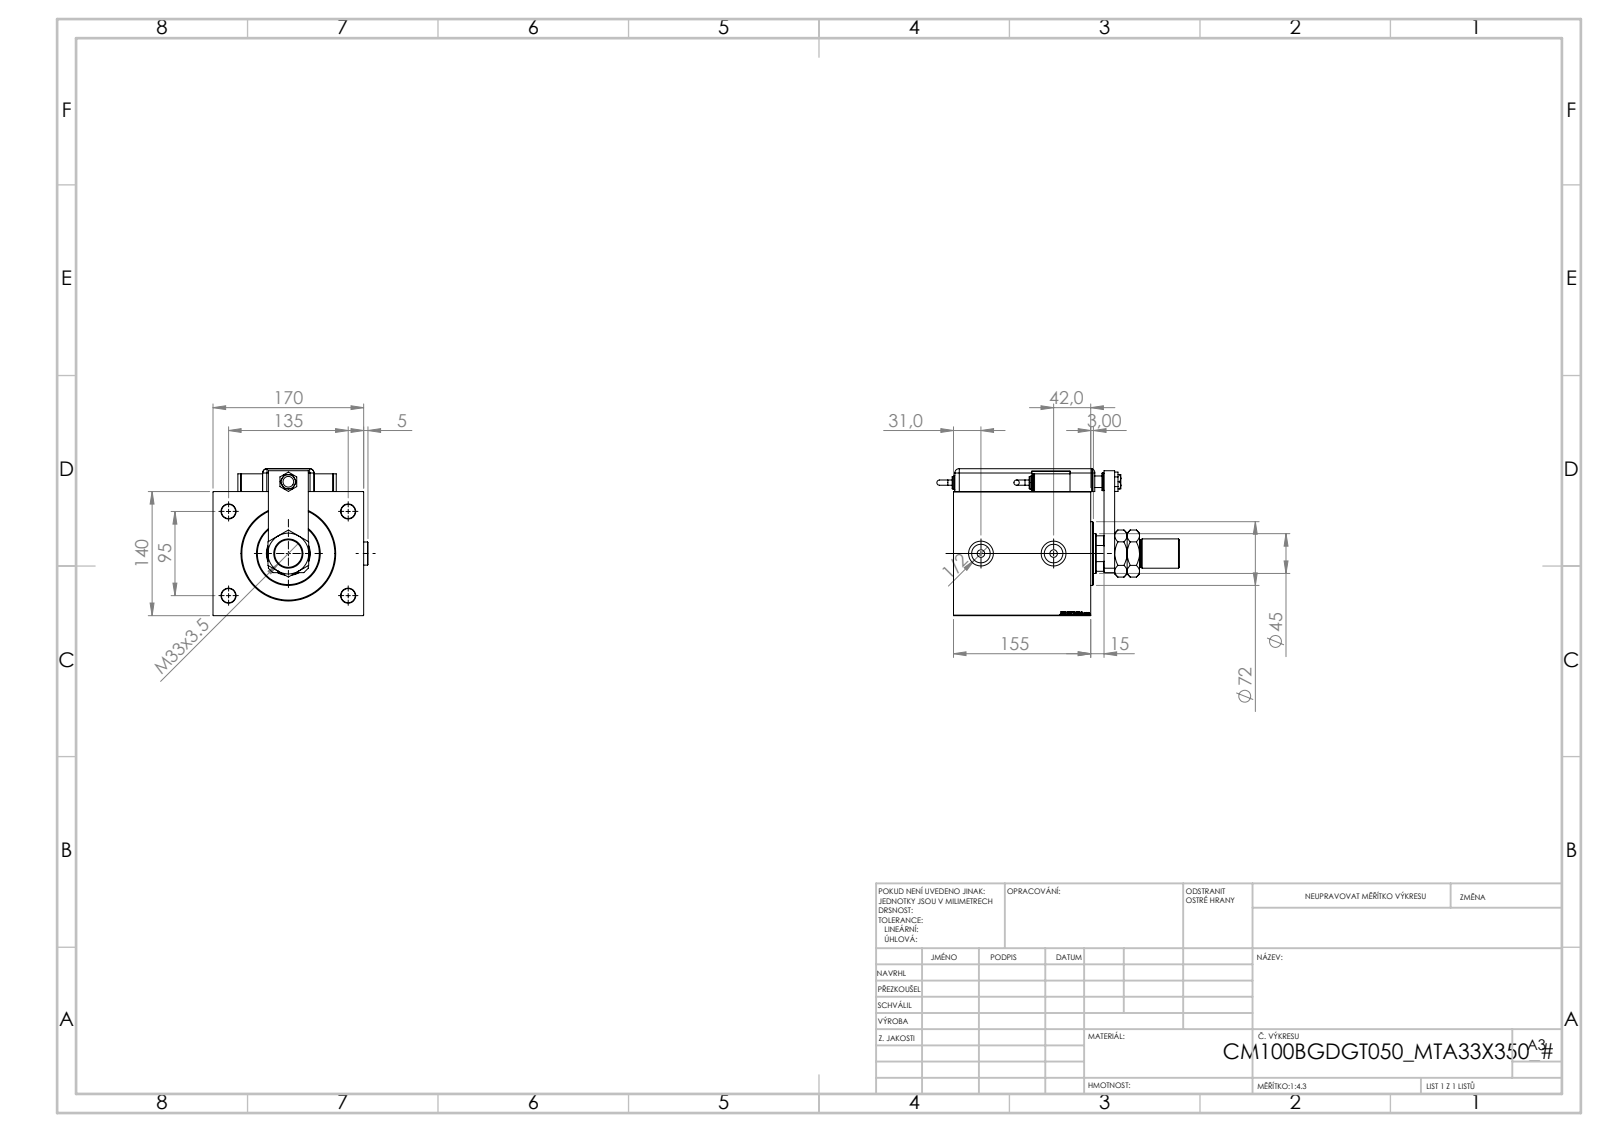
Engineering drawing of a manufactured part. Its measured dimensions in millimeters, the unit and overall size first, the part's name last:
Units: millimetres
Overall size (bounding box): 273.76 × 174.9 × 165.8
Round holes (diameter × count): ⌀16 ×4, ⌀4 ×2, ⌀8 ×2, ⌀8.5 ×2, ⌀20.96 ×2, ⌀28 ×2, ⌀12 ×1, ⌀13 ×1, ⌀14 ×1, ⌀31.5 ×1, ⌀33 ×1, ⌀45 ×1
Round bosses / shafts (diameter × count): ⌀20 ×3, ⌀26 ×2, ⌀16 ×2, ⌀14 ×2, ⌀6 ×2, ⌀72 ×1, ⌀31 ×1
Partial cylindrical surfaces — rounded edges, fillets, slot ends (radius × count): R5 ×9, R10 ×1, R22 ×1
Main face-to-face distances: 140, 170, 155, 3, 26, 129, 15, 114, 1.5, 25.8
Hole centre spacings: 82.54, 75.36, 95, 135, 145.15, 165.08, 20, 81
Volume: 3 595 000 mm³ · Surface area: 366 304 mm²
Bodies: 16 solids, 1371 faces (657 planar, 131 cylindrical, 583 other)
Part name (STEP PRODUCT): TYC; MAGNETIC SWITCH Q; NUT_D19; V450CM_B_VCP (+7 more)
STEP written by: SolidWorks 2019 (CONFIG_CONTROL_DESIGN)
